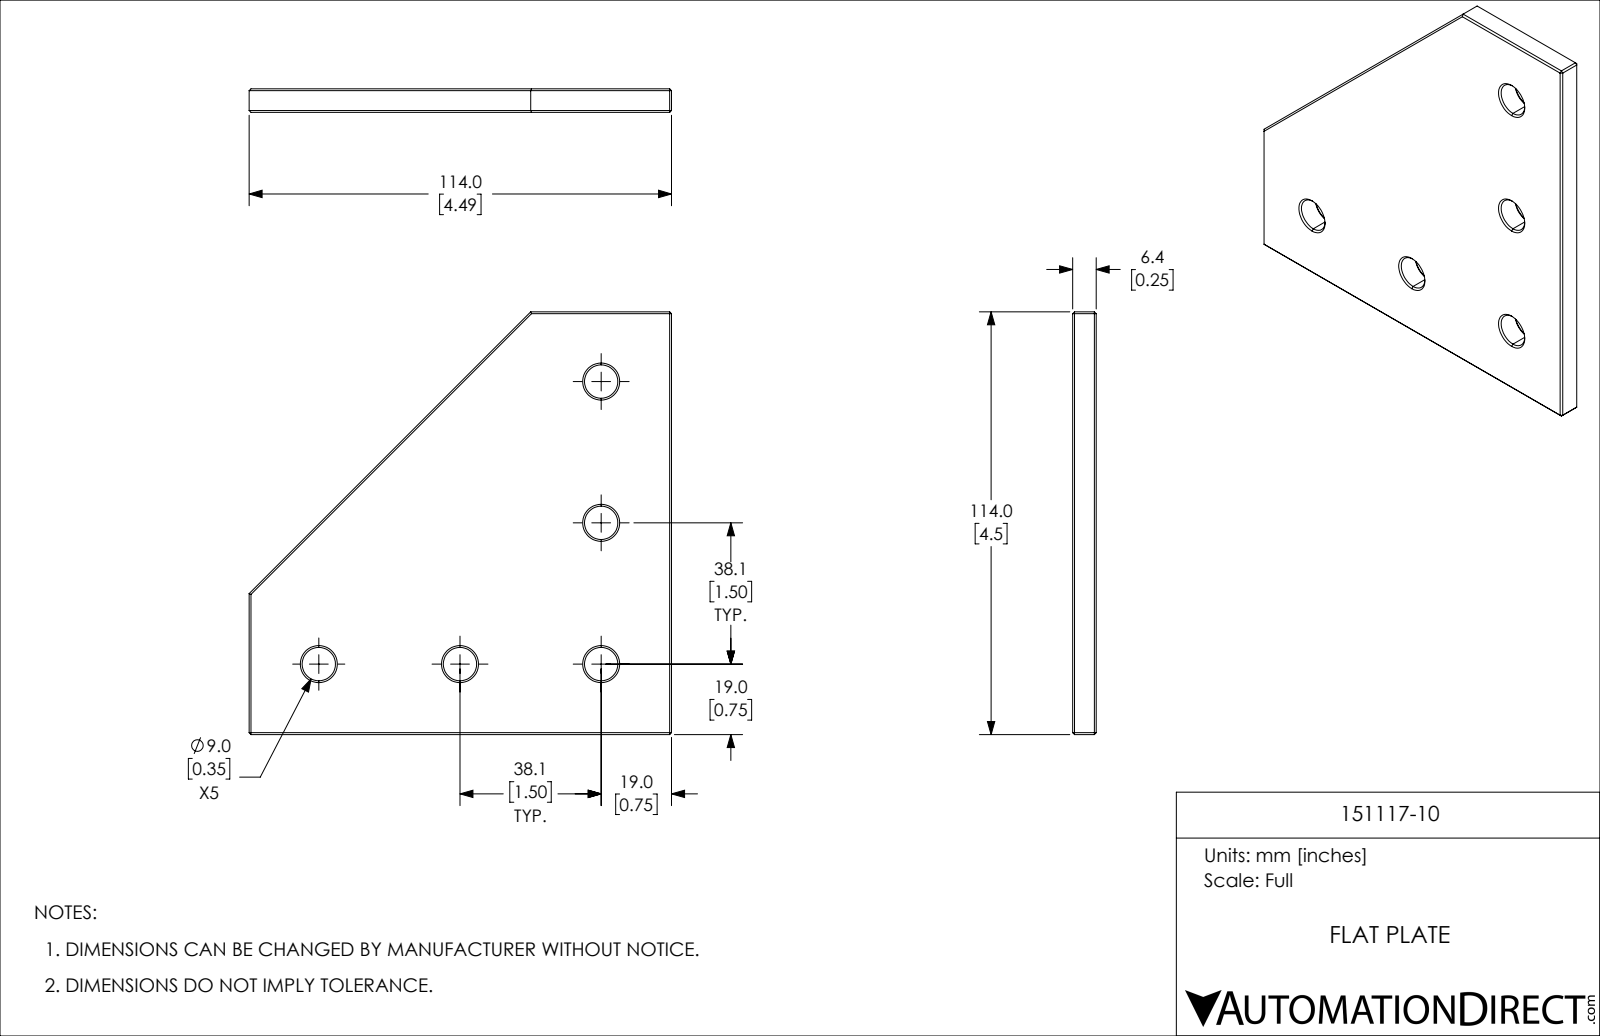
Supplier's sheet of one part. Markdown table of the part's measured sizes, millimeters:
| quantity | value |
| --- | --- |
| part name | 151117-10 |
| STEP written by | SolidWorks 2024 (CONFIG_CONTROL_DESIGN) |
| units | millimeters |
| bodies | 1 solid, 56 faces (26 planar, 10 cylindrical, 20 other) |
| overall size | 114 × 114 × 6.35 |
| volume | 62 025 mm³ |
| surface area | 22 764 mm² |
| round holes (diameter × count) | 9 × 5 |
| main face-to-face distances | 6.35, 114, 84.38, 107.11, 160.48, 134.06 |
| hole center spacings | 38.1, 76.2, 85.19, 53.88, 107.76 |
